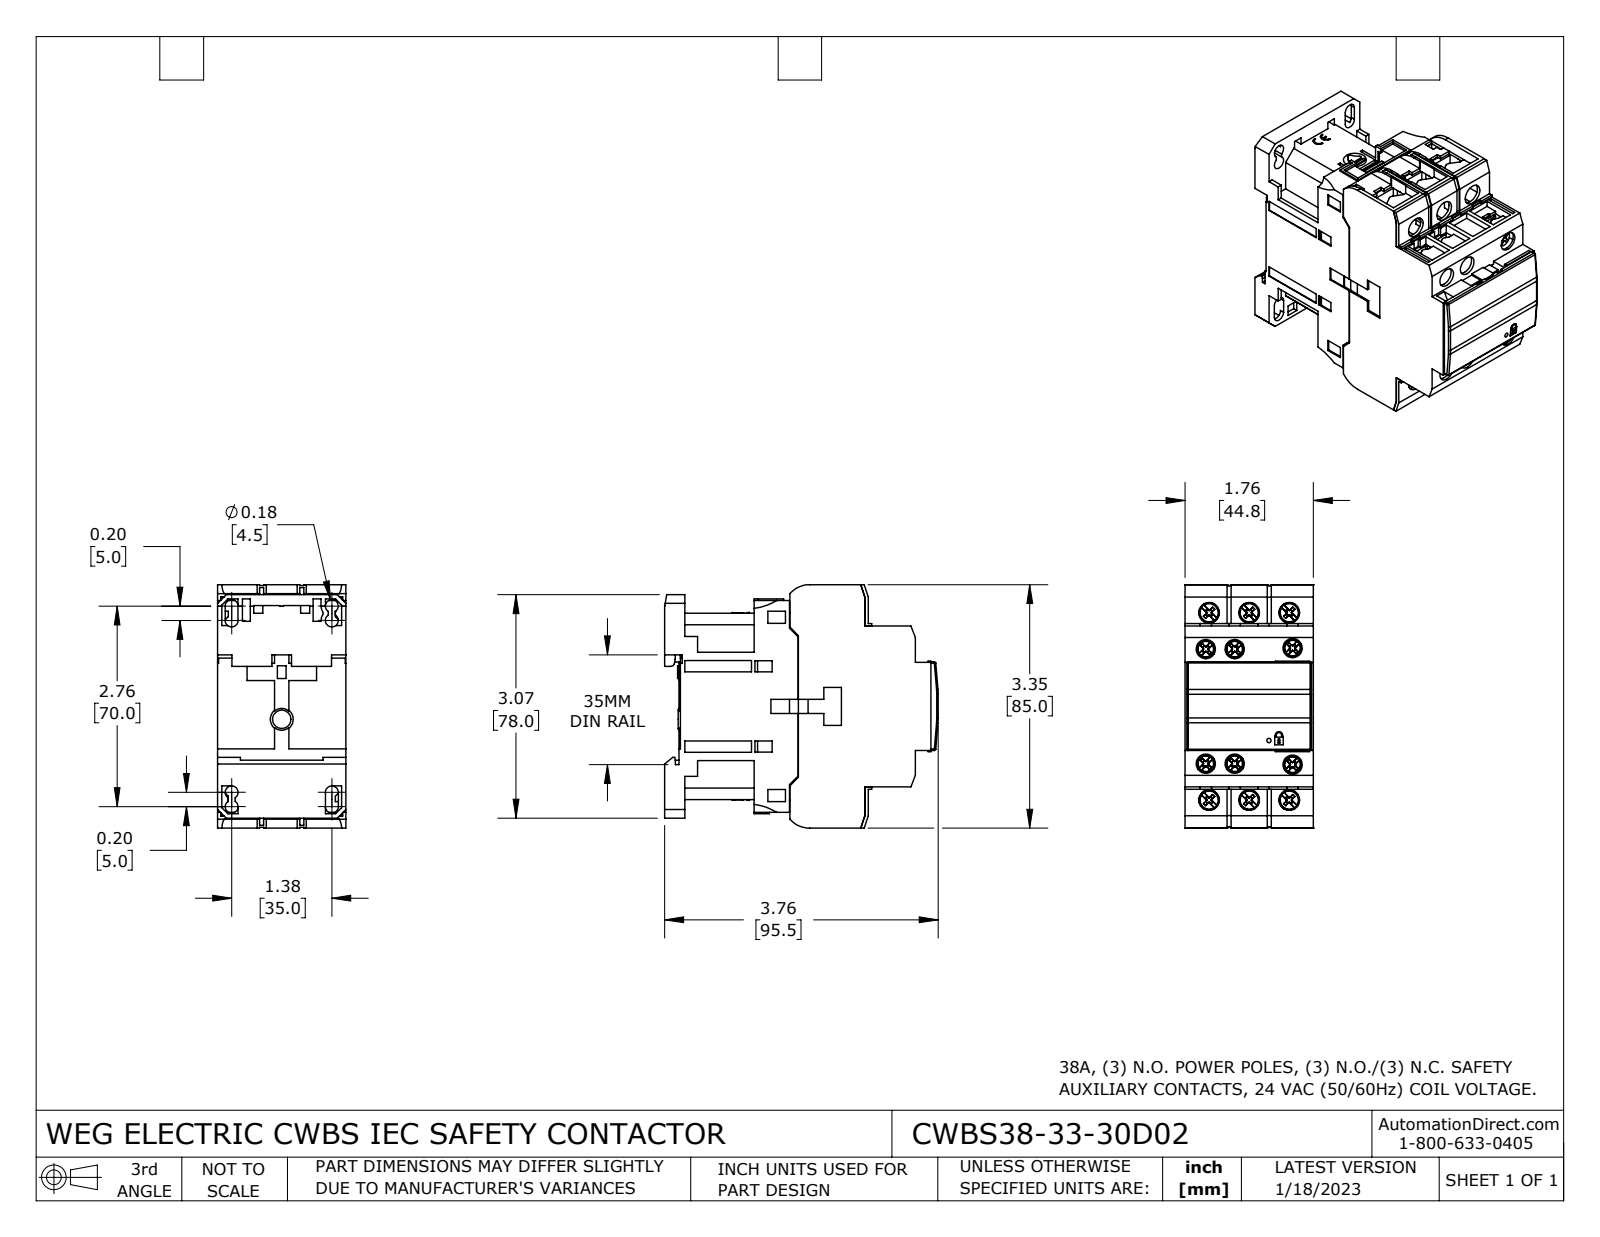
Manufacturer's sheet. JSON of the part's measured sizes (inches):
{"part_name": "CWBS38-33-30D02", "step_written_by": "SolidWorks 2021 (CONFIG_CONTROL_DESIGN)", "units": "inches", "bodies": {"solids": 42, "faces": 2461, "planar": 1808, "cylindrical": 446, "other": 207}, "overall_size": [3.76, 3.346, 1.764], "volume_in3": 14.49, "surface_area_in2": 108.8, "round_holes": [[0.124, 6], [0.142, 6], [0.264, 6], [0.283, 6], [0.177, 4], [0.059, 1]], "round_bosses_or_shafts": [[0.201, 6], [0.169, 6], [0.157, 6], [0.138, 6], [0.107, 4], [0.107, 2]], "partial_cylinders_radius": [[0.02, 42], [0.028, 24], [0.071, 12], [0.081, 12], [0.964, 12], [1.079, 12], [2.128, 12], [3.127, 12]], "face_to_face_distances": [1.764, 0.047, 1.691, 0.132, 1.823, 0.024, 0.217, 3.445, 0.276, 1.717], "hole_center_spacings": [0.551, 2.633, 2.575, 0.165, 0.174, 0.197, 0.398, 0.488]}
